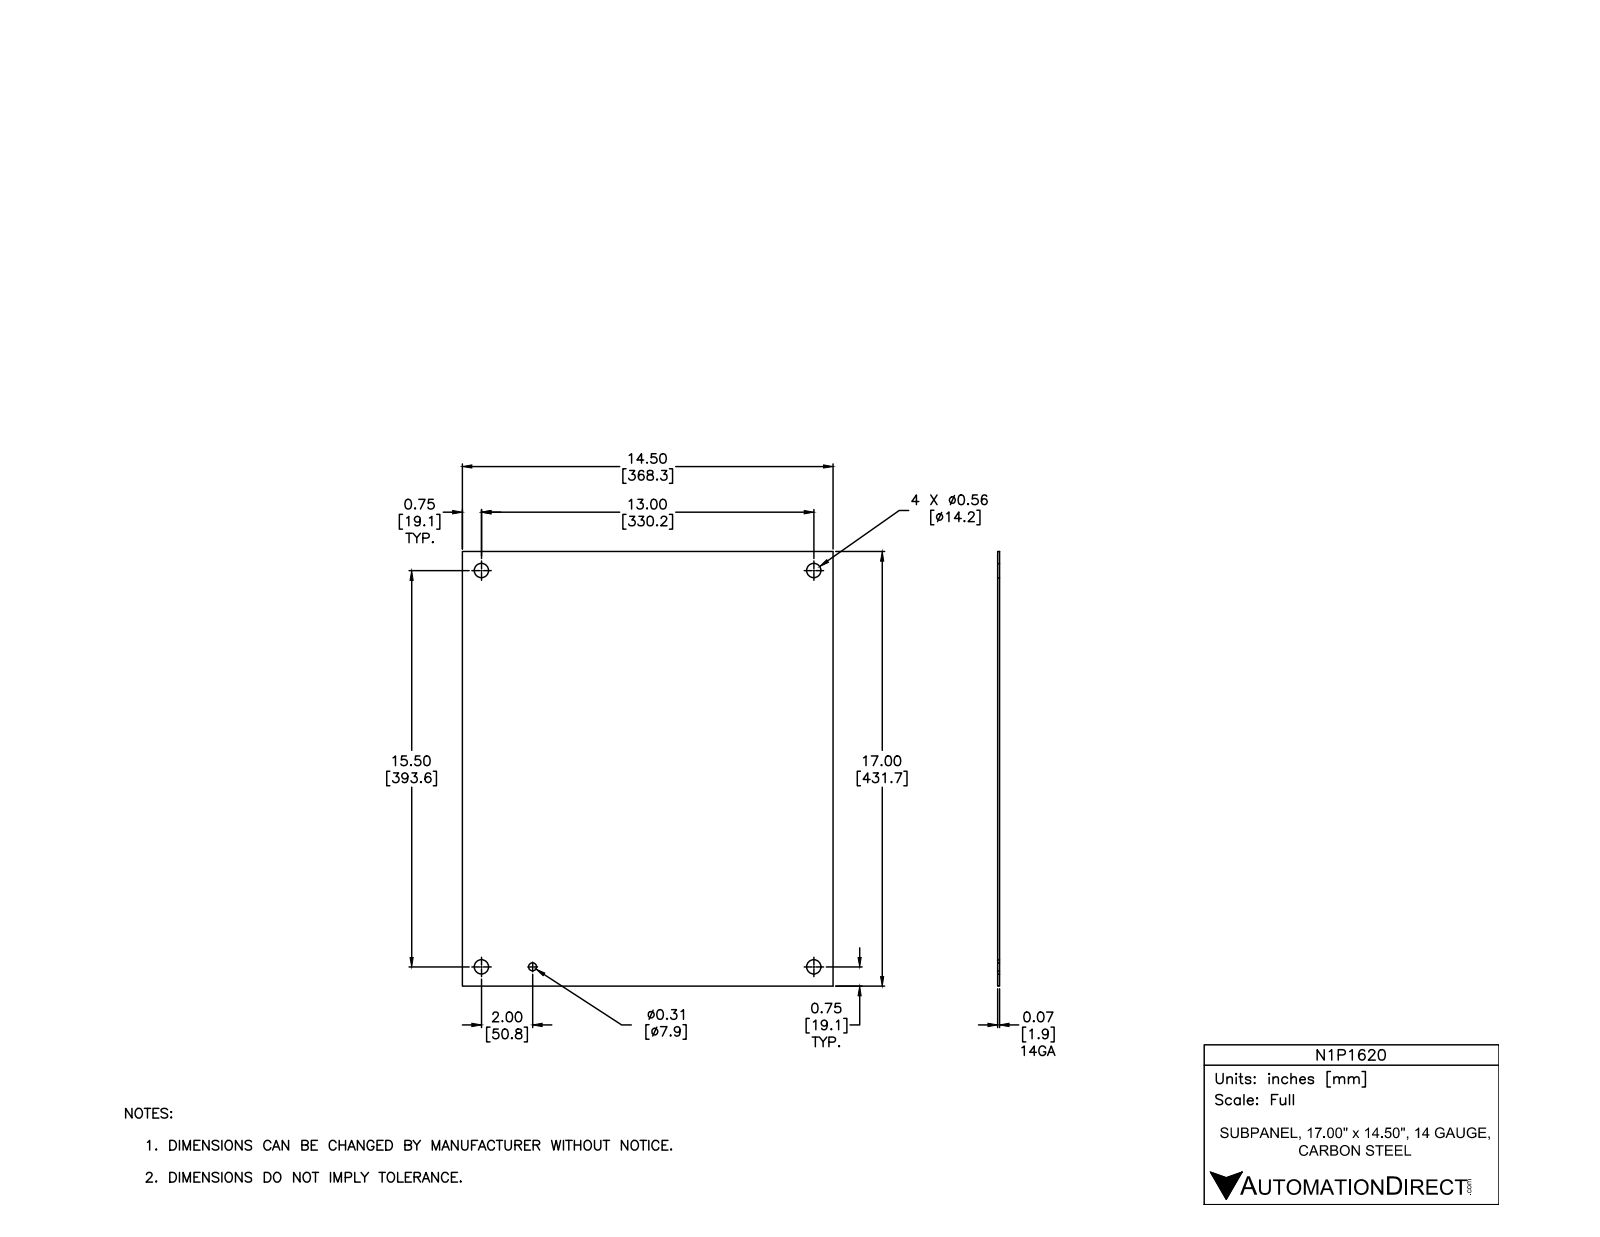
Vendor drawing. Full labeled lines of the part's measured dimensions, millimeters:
Part name (STEP PRODUCT): N1P1620-1
STEP written by: Autodesk Inventor 2012 (AUTOMOTIVE_DESIGN)
Units: millimetres
Bodies: 1 solid, 11 faces (6 planar, 5 cylindrical, 0 other)
Overall size (bounding box): 431.8 × 368.3 × 1.9
Volume: 297 600 mm³ · Surface area: 320 100 mm²
Round holes (diameter × count): ⌀14.3 ×4, ⌀7.9 ×1
Main face-to-face distances: 1.9, 368.3, 431.8
Hole centre spacings: 330.2, 393.7, 513.8, 50.8, 279.4, 397, 482.8
